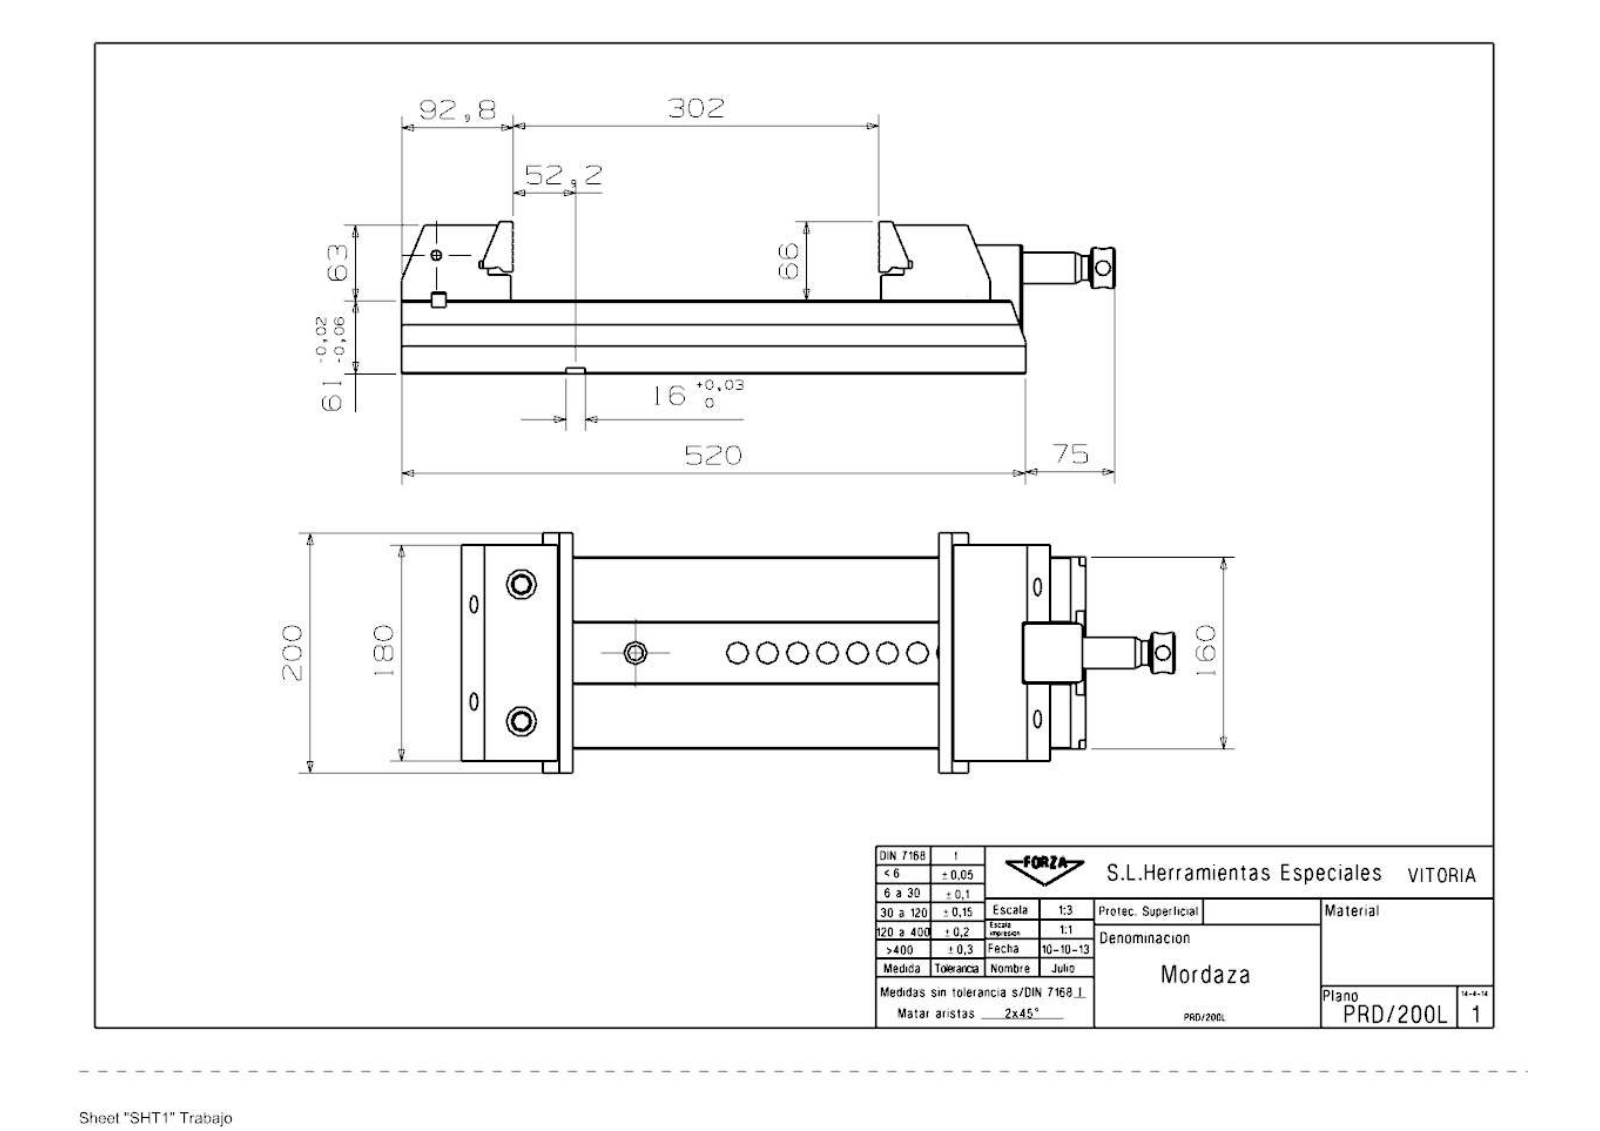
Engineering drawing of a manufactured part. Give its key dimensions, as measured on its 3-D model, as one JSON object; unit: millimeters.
{"part_name": "30150070 Montaje Taco Hus; PRD_200L_Mordaza", "step_written_by": "SIEMENS PLM Software NX 9.0 (CONFIG_CONTROL_DESIGN)", "units": "millimeters", "bodies": {"solids": 11, "faces": 456, "planar": 280, "cylindrical": 126, "other": 50}, "overall_size": [594.42, 200, 126.95], "volume_mm3": 5899000, "surface_area_mm2": 619049, "round_holes": [[15, 6], [5.19, 5], [13, 5], [19, 5], [6.99, 4], [8.5, 4], [10, 4], [8.78, 3], [10.58, 3], [12, 2], [12.38, 2], [14.38, 2]], "round_bosses_or_shafts": [[34, 1], [33.8, 1], [26, 1], [20, 1], [16.5, 1]], "partial_cylinders_radius": [[0.4, 24], [8, 4], [20, 4], [1.6, 2], [6, 2], [7, 2], [4, 1], [9, 1]], "face_to_face_distances": [61, 29.2, 31.8, 63, 45, 160, 124, 94.8, 10, 1.1], "hole_center_spacings": [14.5, 95.5, 81, 110, 68, 16.47, 16.55, 24.52]}
